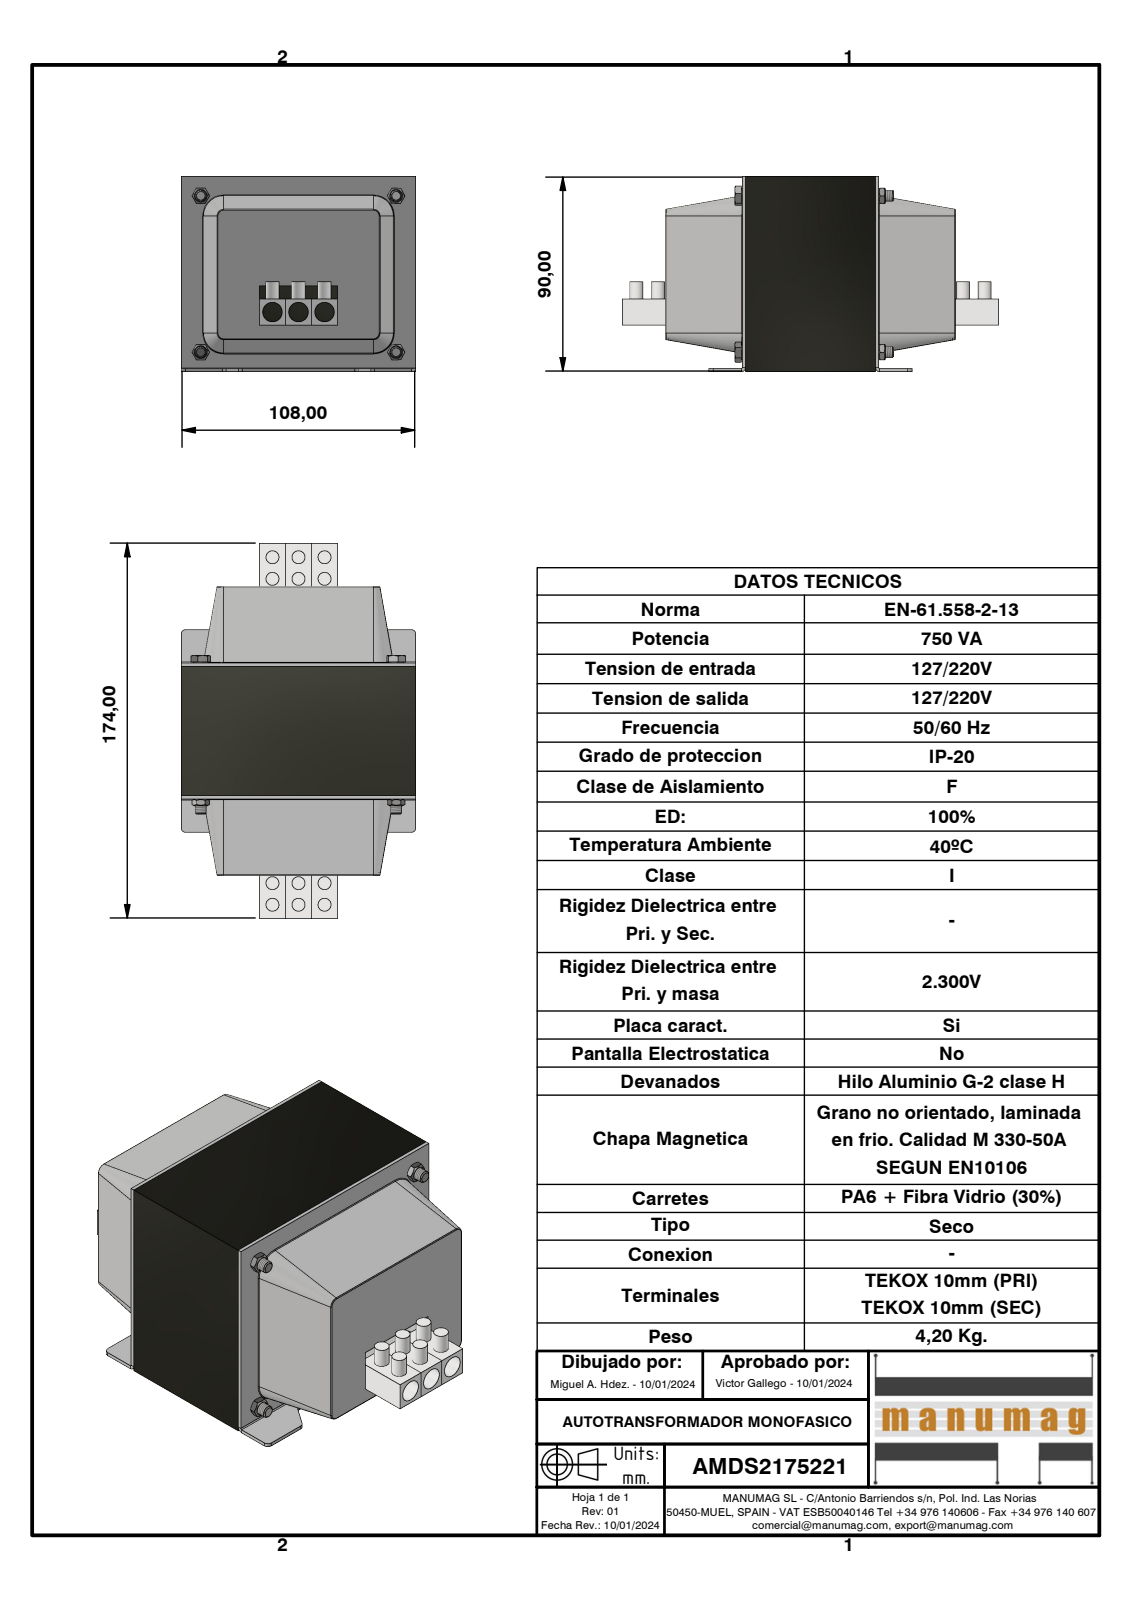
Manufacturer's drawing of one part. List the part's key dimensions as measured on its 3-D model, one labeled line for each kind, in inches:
Part name (STEP PRODUCT): AMDS217521; DIN 933 - M5 x 70; DIN 934 - M4 x 0,7; TAPA RC36 VENTANA 3 ELEMENTOS 10 CON FICHAS (+4 more)
STEP written by: Autodesk Inventor 2023 (AUTOMOTIVE_DESIGN)
Units: inches
Bodies: 17 solids, 352 faces (194 planar, 78 cylindrical, 80 other)
Overall size (bounding box): 6.85 × 4.252 × 3.543
Volume: 31.19 in³ · Surface area: 240.7 in²
Round holes (diameter × count): ⌀0.128 ×4, ⌀0.197 ×4, ⌀0.22 ×4, ⌀0.354 ×3
Round bosses / shafts (diameter × count): ⌀0.236 ×12, ⌀0.264 ×4, ⌀0.18 ×4
Partial cylindrical surfaces — rounded edges, fillets, slot ends (radius × count): R0.015 ×16, R0.079 ×14, R0.02 ×2
Main face-to-face distances: 0.709, 0.059, 2.835, 1.398, 3.819, 3.543, 2.362, 1.417, 2.126, 3.76
Hole centre spacings: 0.472, 1.489, 1.915, 2.359, 2.476, 2.754, 2.835, 3.079
